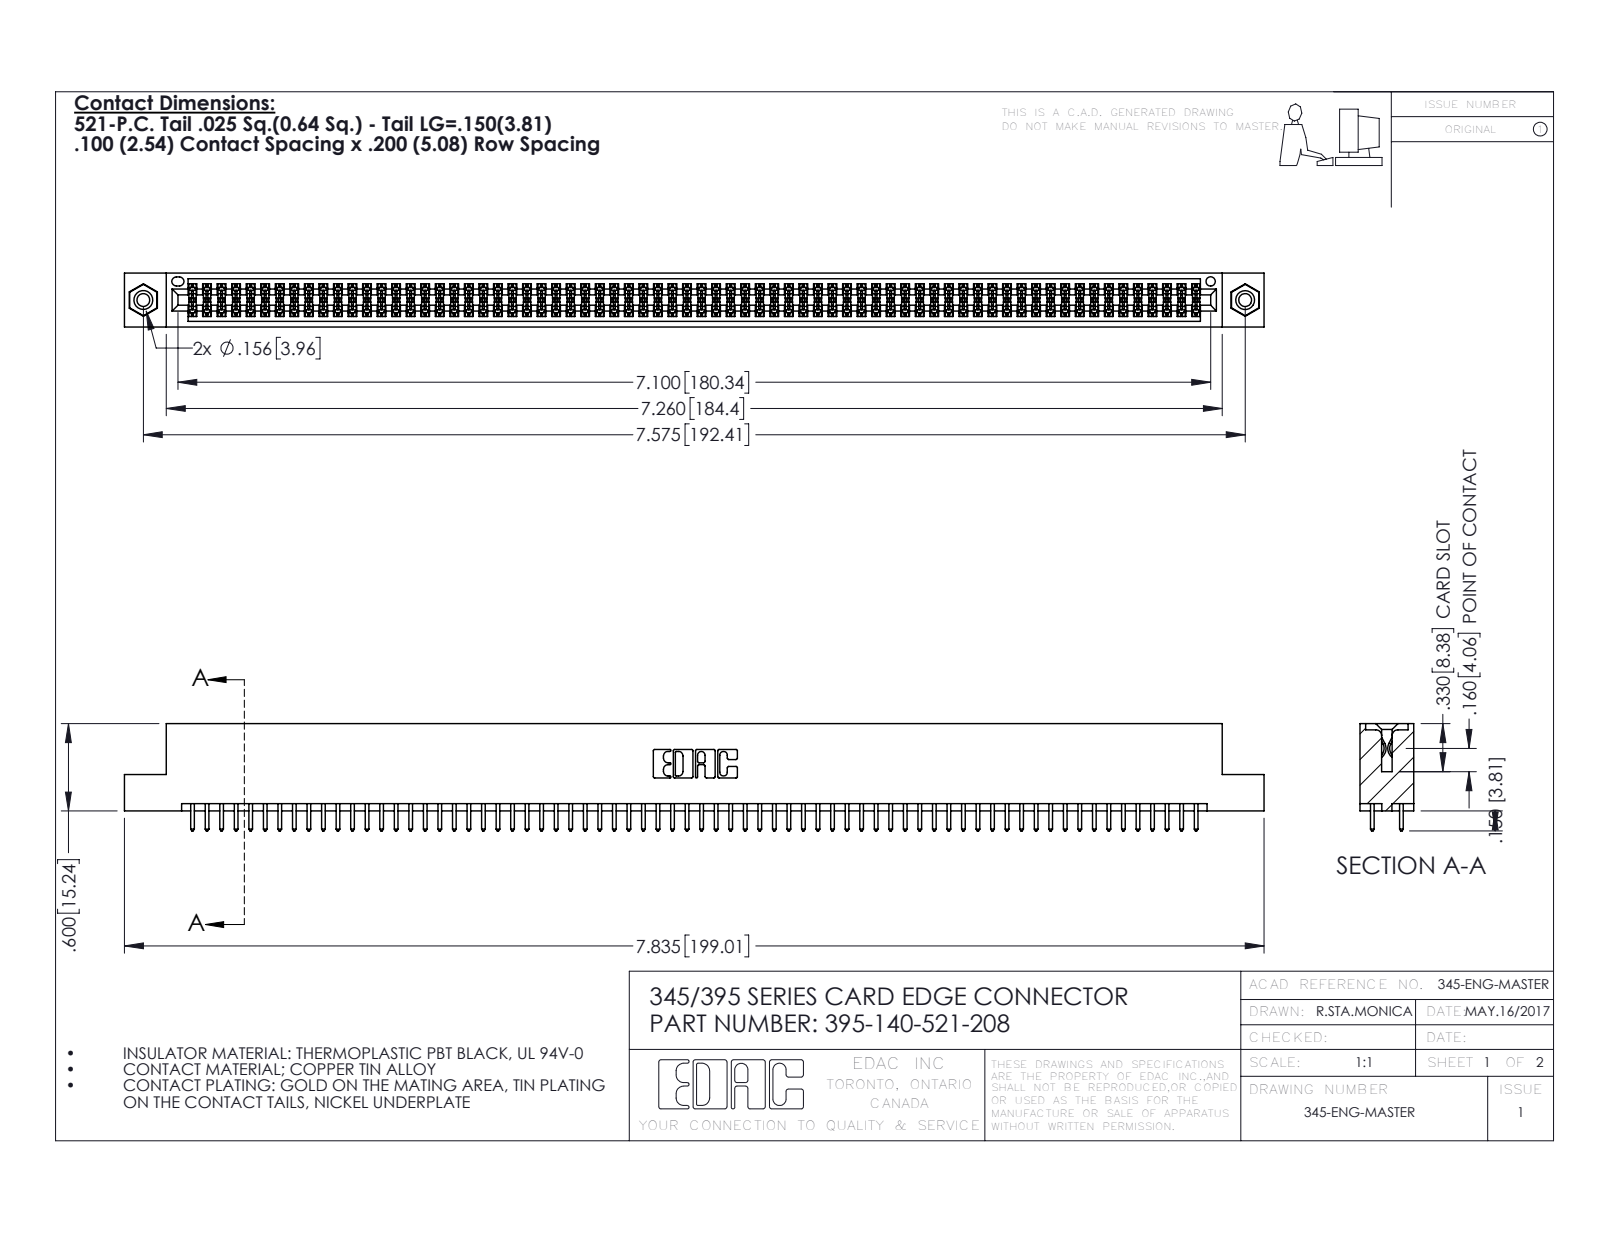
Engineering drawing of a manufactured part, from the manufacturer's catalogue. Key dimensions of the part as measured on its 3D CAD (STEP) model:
Part name (STEP PRODUCT): 345 Part_Flush Mounting Lugs - 0.156 Dia-TI; 395-140-521-208; 345-250-001_345-250-003-102; 345-292-001_345-293-121
STEP written by: SolidWorks 2016 (CONFIG_CONTROL_DESIGN)
Units: inches
Bodies: 143 solids, 7186 faces (4732 planar, 2438 cylindrical, 16 other)
Overall size (bounding box): 7.835 × 0.737 × 0.37
Volume: 1.192 in³ · Surface area: 45.03 in²
Round holes (diameter × count): ⌀0.089 ×2, ⌀0.125 ×2, ⌀0.156 ×2, ⌀0.064 ×1
Round bosses / shafts (diameter × count): ⌀0.155 ×2
Partial cylindrical surfaces — rounded edges, fillets, slot ends (radius × count): R0.006 ×210, R0.01 ×140, R0.01 ×22, R0.007 ×6, R0.031 ×6, R0.026 ×3, R0.014 ×2, R0.019 ×2
Main face-to-face distances: 0.072, 0.298, 0.2, 0.098, 0.272, 0.025, 0.37, 0.225, 0.175, 0.149
Hole centre spacings: 0.27, 7.339, 7.575
